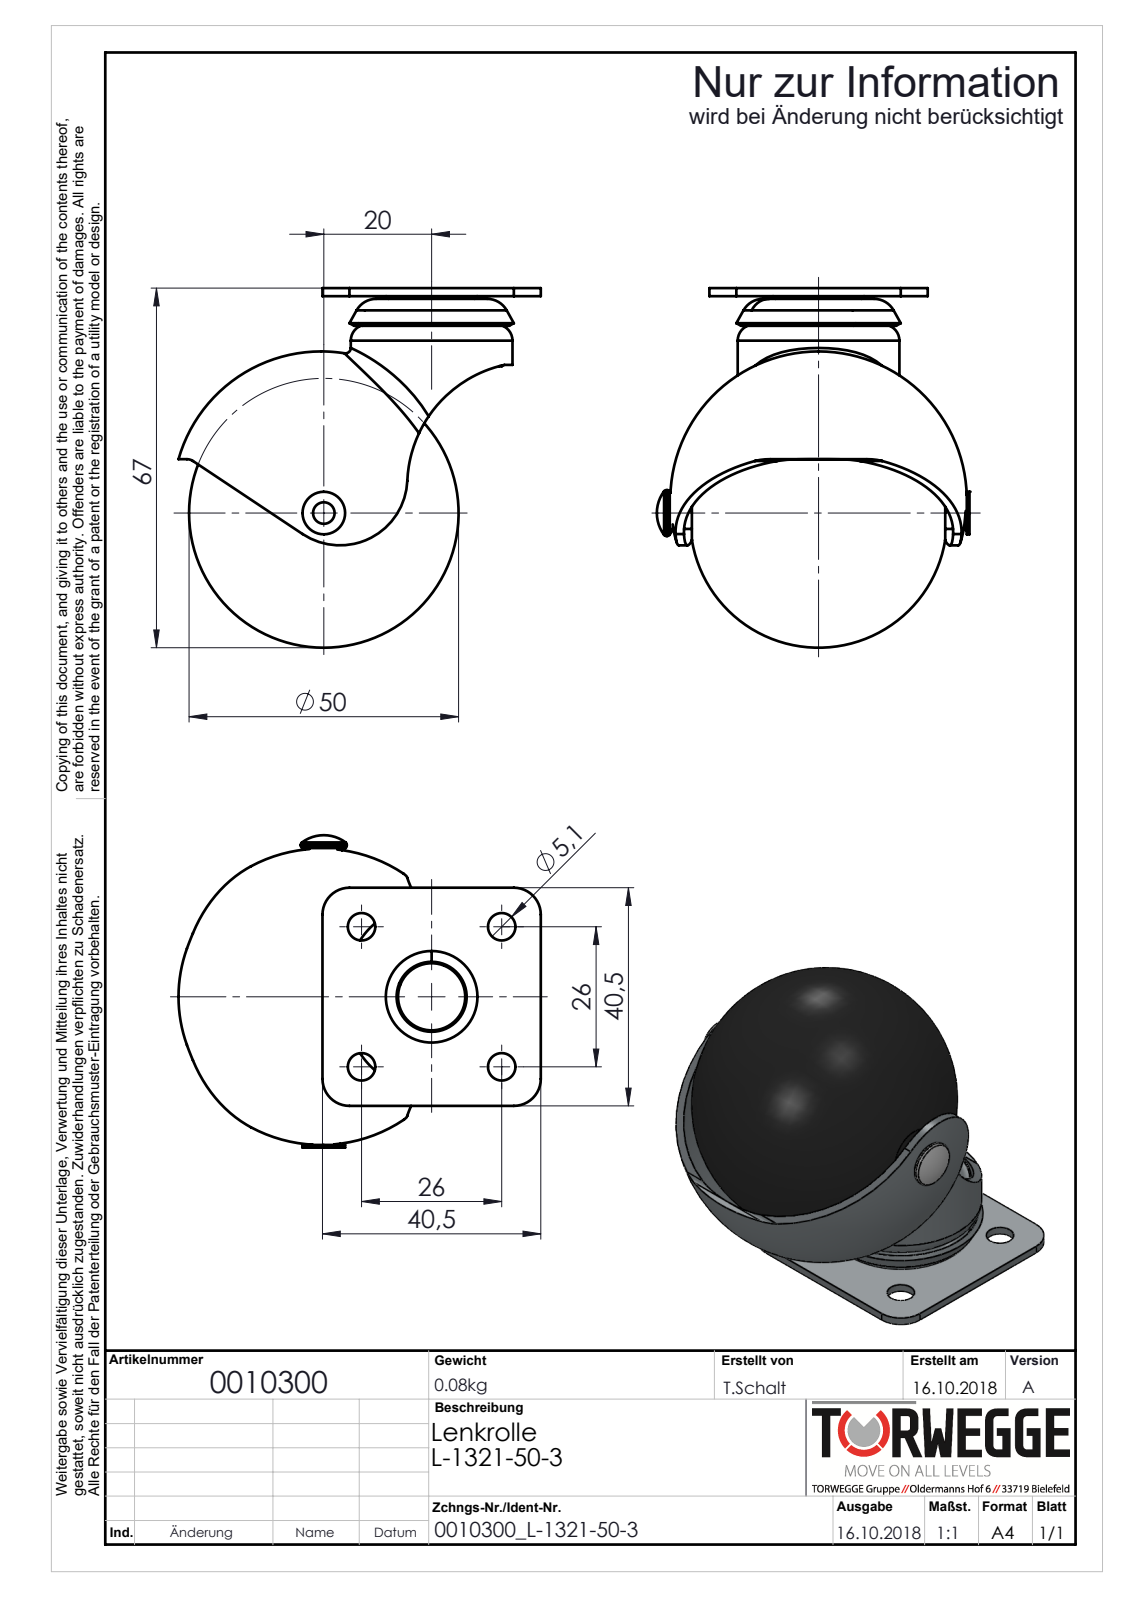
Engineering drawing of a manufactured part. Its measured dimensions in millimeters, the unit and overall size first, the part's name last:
Units: millimetres
Overall size (bounding box): 67.21 × 66.75 × 58
Round holes (diameter × count): ⌀5.1 ×4, ⌀4 ×1, ⌀6 ×1, ⌀6.1 ×1, ⌀9 ×1, ⌀9.5 ×1, ⌀11.2 ×1, ⌀27 ×1
Round bosses / shafts (diameter × count): ⌀30 ×1, ⌀26.1 ×1, ⌀11 ×1, ⌀8.9 ×1, ⌀8.5 ×1, ⌀7.9 ×1, ⌀5.9 ×1
Partial cylindrical surfaces — rounded edges, fillets, slot ends (radius × count): R5 ×4, R2.01 ×1, R12.5 ×1, R23.03 ×1
Main face-to-face distances: 1.5, 1, 2.5, 3.5, 0.5, 4, 2, 6.5, 3.25, 43.75
Hole centre spacings: 18.38, 26, 36.77
Volume: 75 238 mm³ · Surface area: 26 695 mm²
Bodies: 9 solids, 152 faces (25 planar, 52 cylindrical, 75 other)
Part name (STEP PRODUCT): F8_5_32.stp; F850.stp; F8_1_8.stp; 07089.stp (+8 more)
STEP written by: SolidWorks 2018 (AUTOMOTIVE_DESIGN)
